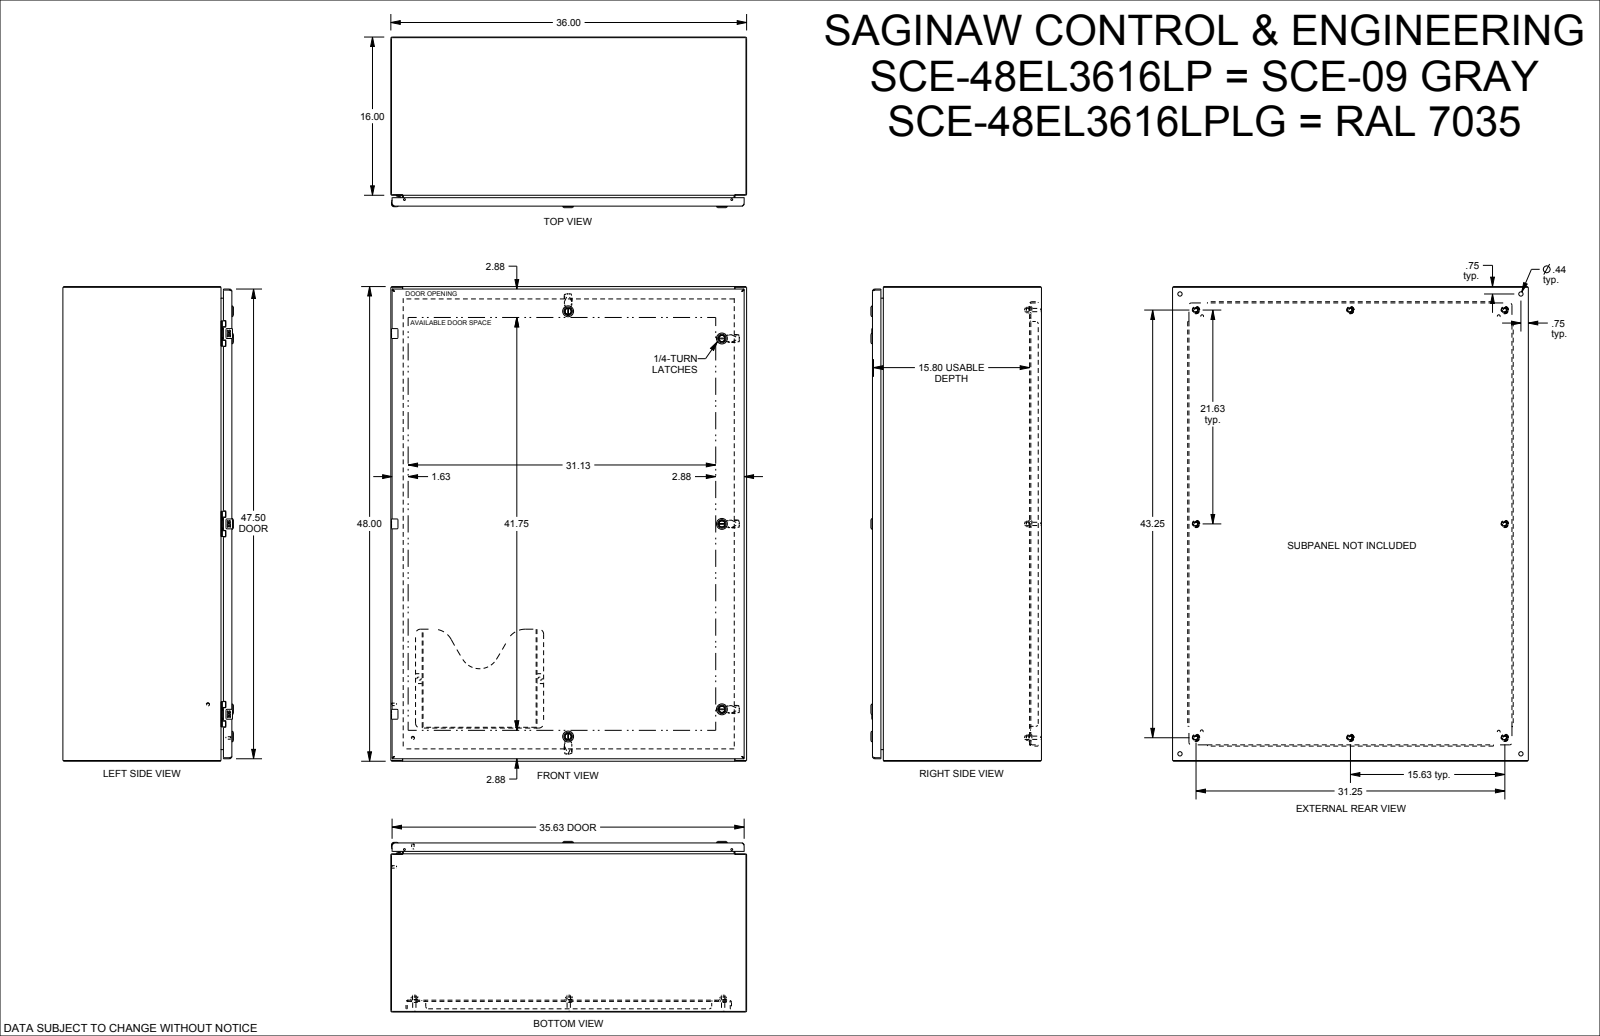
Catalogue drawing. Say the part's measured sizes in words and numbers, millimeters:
The part is named "SCE-48EL3616LP". Its 3-D file was written by "SolidWorks 2019 (CONFIG_CONTROL_DESIGN)". It is 0 solids with 4768 faces: 2330 planar, 1319 cylindrical and 1119 other. Overall it measures 1219.2 by 914.4 by 438.3 millimeters. Round holes: 8 of diameter 9.3, 8 of diameter 12.7, 6 of diameter 4.4, 6 of diameter 5.2, 6 of diameter 6.2, 6 of diameter 6.8, 6 of diameter 9.5, 5 of diameter 5, 5 of diameter 8, 5 of diameter 10, 5 of diameter 16.1, 4 of diameter 7.1. Round bosses or shafts: 9 of diameter 4.3, 8 of diameter 9.3, 8 of diameter 8.4, 6 of diameter 6.4, 6 of diameter 6.1, 5 of diameter 28, 5 of diameter 22, 5 of diameter 20.4. Partial cylindrical surfaces (rounded edges, fillets, slot ends): 136 of radius 0.3, 52 of radius 0.3, 52 of radius 0.5, 32 of radius 0.4, 20 of radius 4, 17 of radius 1, 16 of radius 0.6, 16 of radius 2.5. The main face-to-face distances are 1.9, 2.6, 431.7, 429.8, 434.3, 432.4, 1.9, 28.6, 401.2, 912.5. The hole center spacings are 489, 977.9, 1.3, 12.5, 12.5, 25, 463.9, 476.4.
